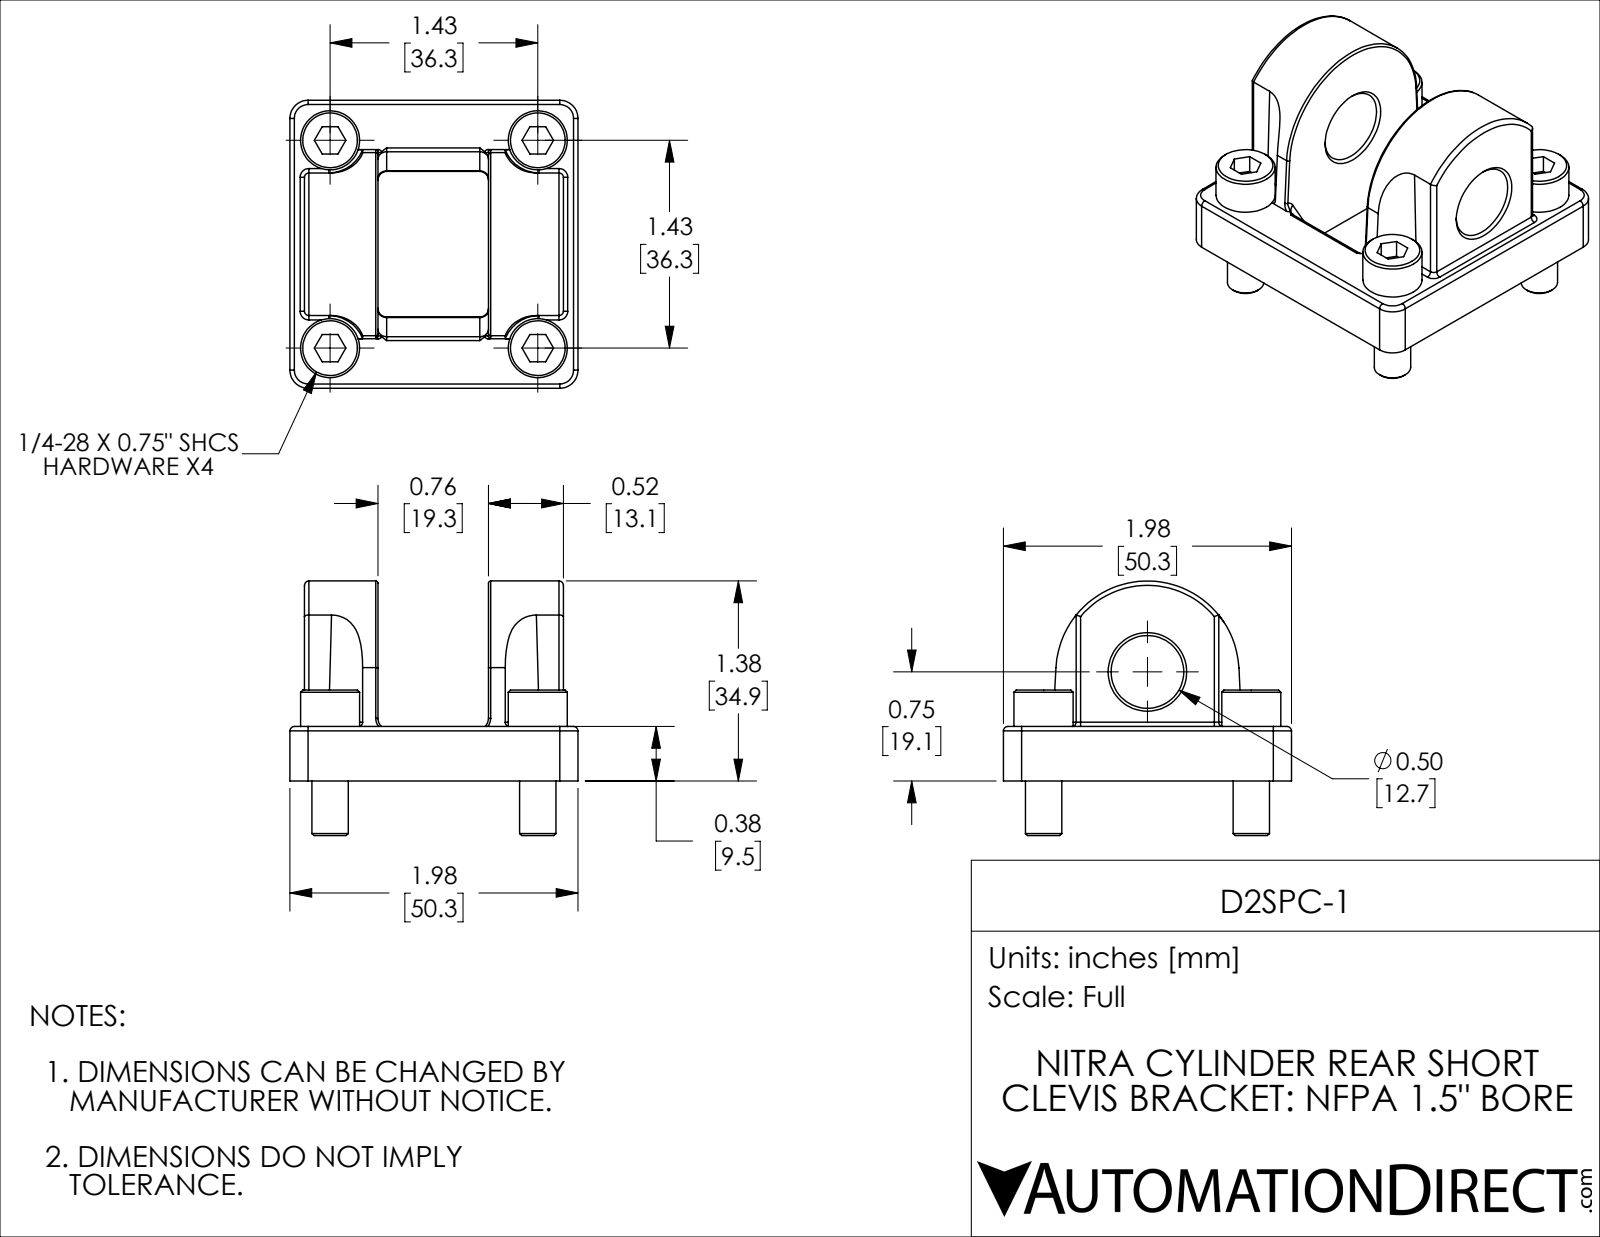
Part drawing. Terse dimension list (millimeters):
name: D2SPC-1
written by: SolidWorks 2019 (CONFIG_CONTROL_DESIGN)
unit: mm
bodies: 5 solids, 182 faces (62 planar, 64 cylindrical, 56 other)
size: 50.3 × 50.3 × 44.5
volume: 34 630 mm³; area: 14 450 mm²
holes: 4× ⌀7.1, 1× ⌀12.7
bosses: 4× ⌀10.3, 4× ⌀6.4
rounds: 16× R0.8, 8× R1.5, 4× R0.4, 4× R3.2, 1× R16
face distances: 9.5, 50.3, 19.3, 2.5, 47.8, 15.4, 34.7, 34.9, 15.6, 12.8
hole spacings: 36.3, 51.3
